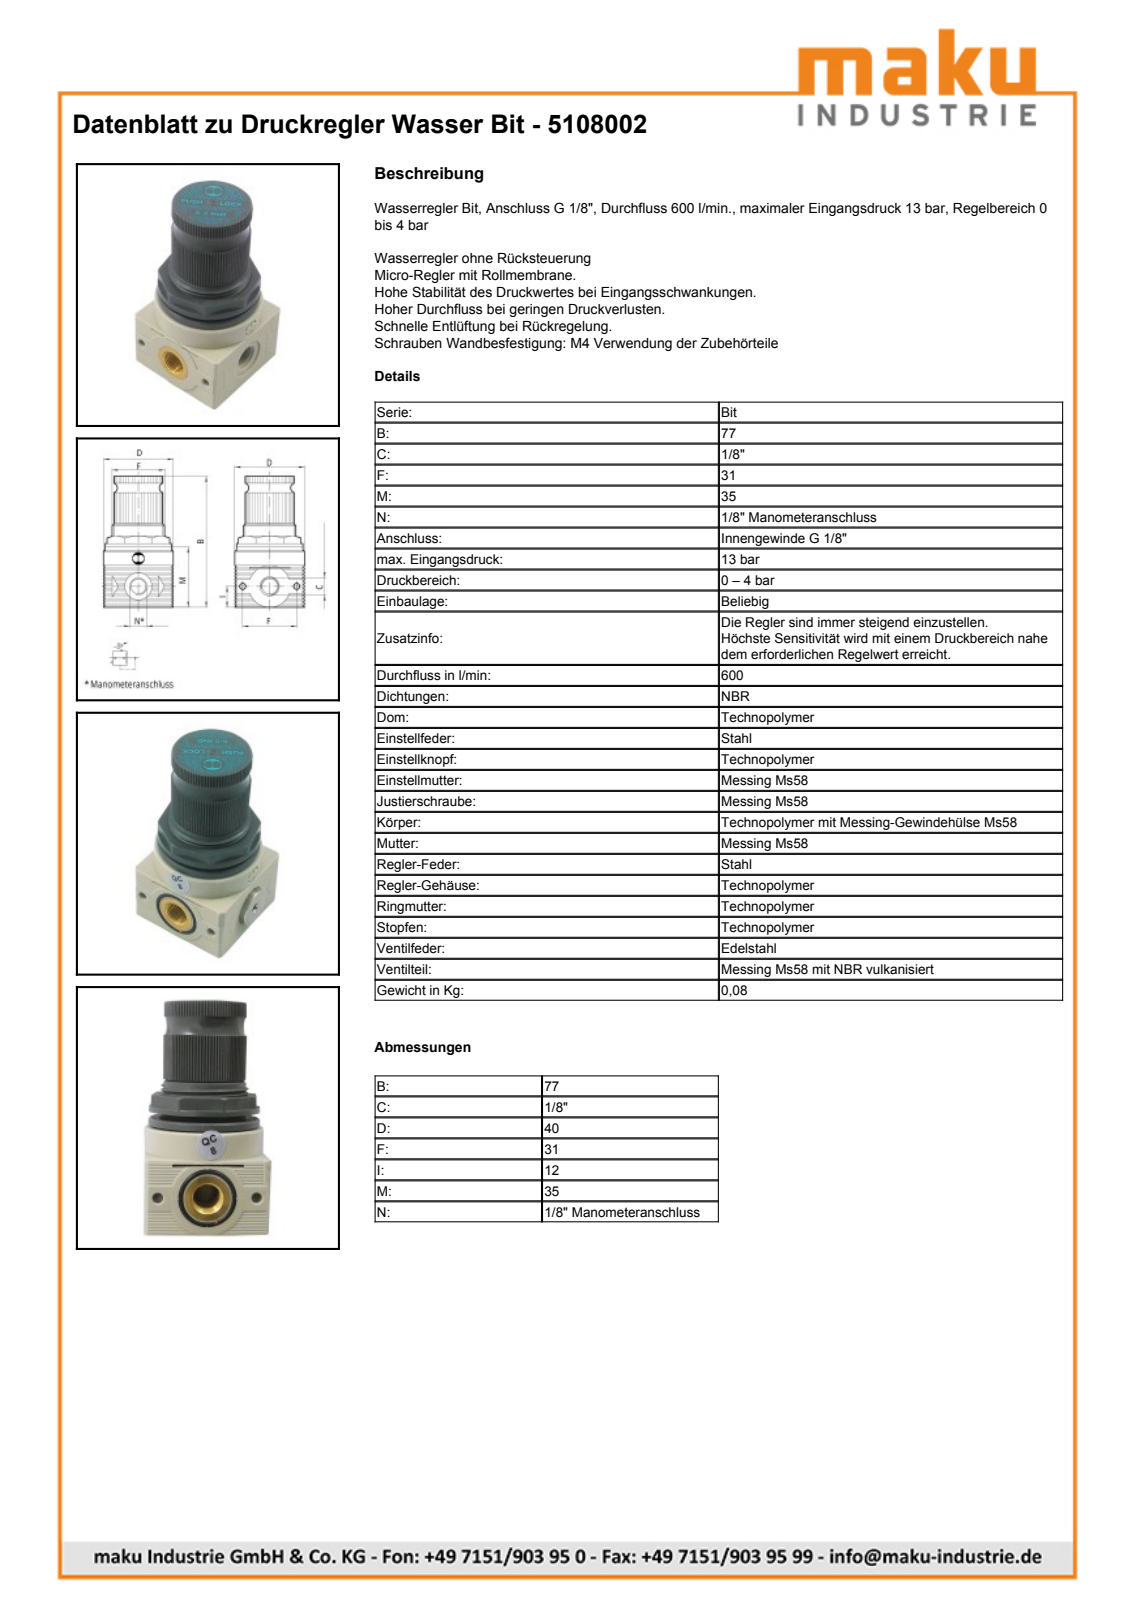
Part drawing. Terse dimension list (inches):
name: 5108002; 5108002-BD; 5108002-KN; 1/8-BIT
written by: PARTsolutions (AUTOMOTIVE_DESIGN)
unit: in
bodies: 3 solids, 127 faces (92 planar, 27 cylindrical, 8 other)
size: 3.031 × 1.634 × 1.575
volume: 4.713 in³; area: 28.17 in²
holes: 2× ⌀0.157, 2× ⌀0.337, 1× ⌀0.61
bosses: 1× ⌀1.571, 1× ⌀1.496, 1× ⌀1.48, 1× ⌀1.181, 1× ⌀1.102, 1× ⌀0.945, 1× ⌀0.591, 1× ⌀0.383
rounds: 1× R0.472
face distances: 1.26, 1.575, 0.039, 0.354, 0.394, 1.573, 3.031, 1.772, 1.535, 0.748
hole spacings: 0.61, 1.22
